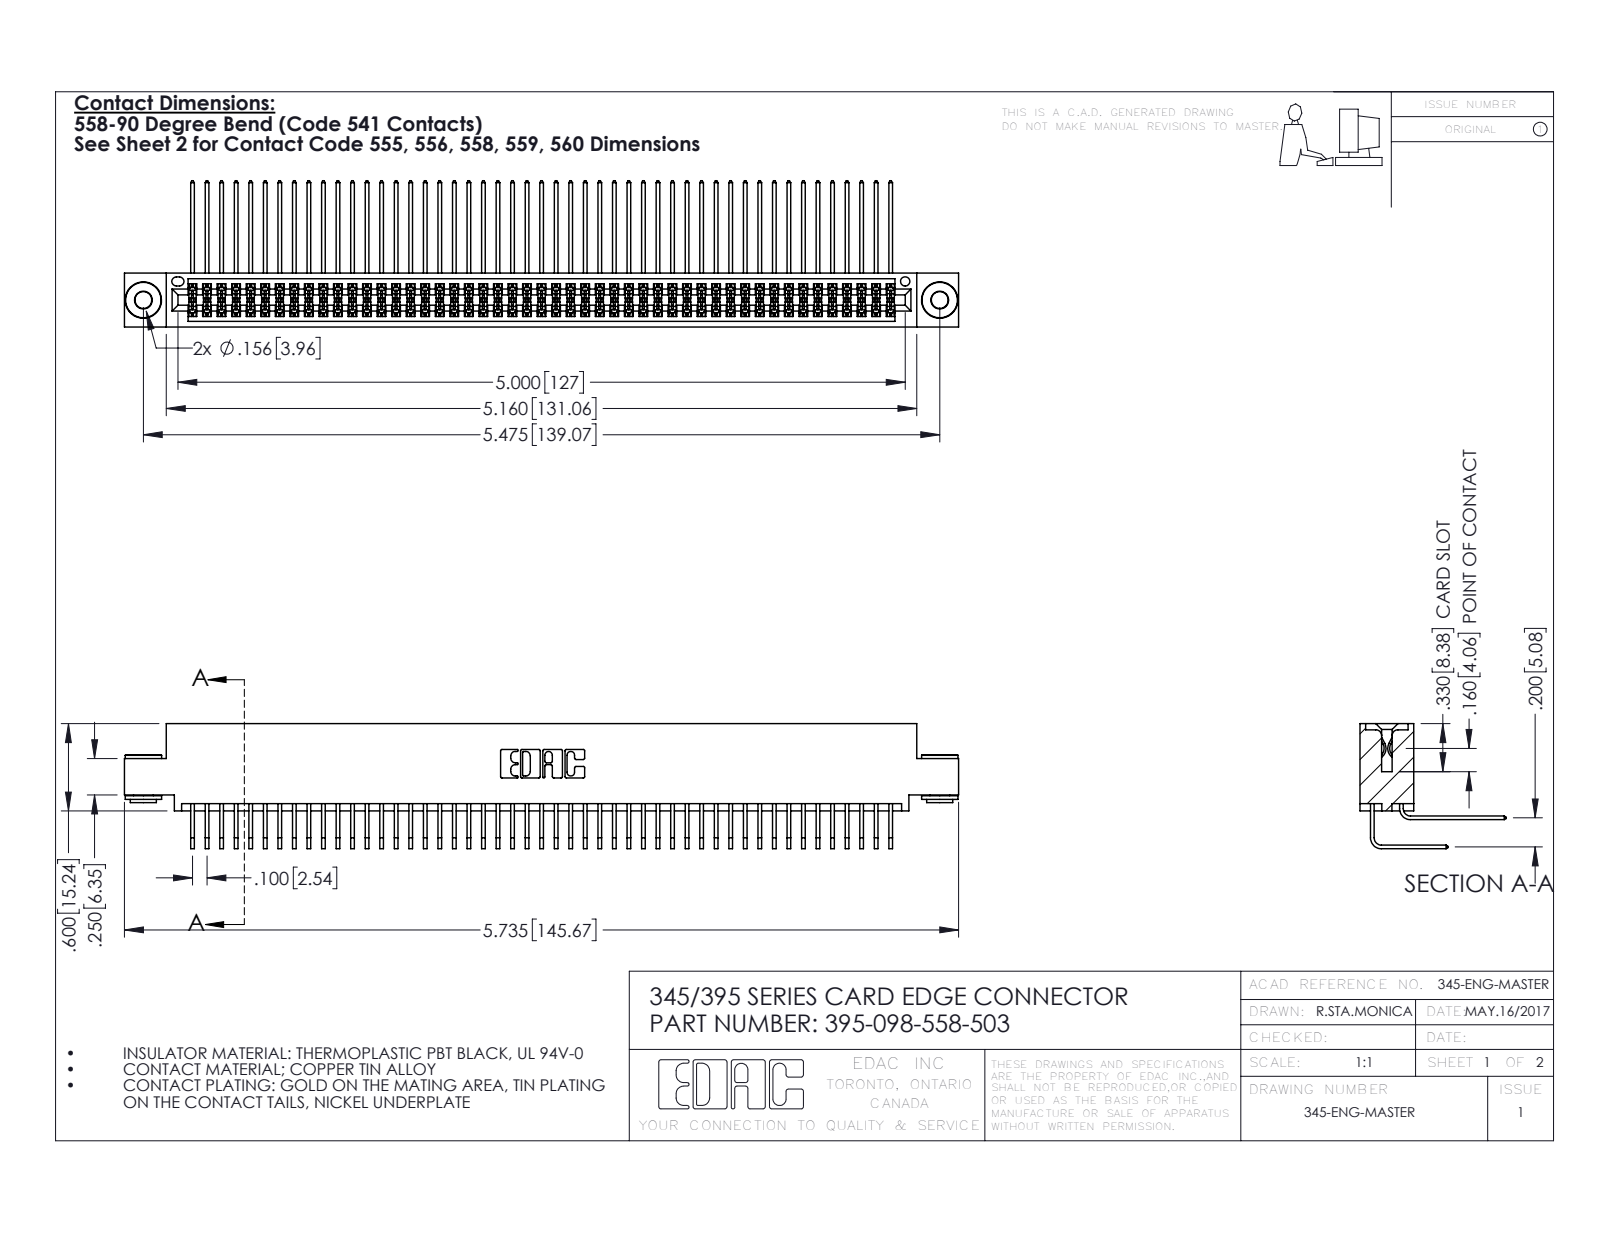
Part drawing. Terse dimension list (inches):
name: 345-292-001_558 Tail - 2; 345 Part_0.110 Offset - 0.156 Dia-TH; 345-250-002_345-250-002-102; 395-098-558-503 (+1 more)
written by: SolidWorks 2016 (CONFIG_CONTROL_DESIGN)
unit: in
bodies: 101 solids, 5264 faces (3524 planar, 1732 cylindrical, 8 other)
size: 5.735 × 1.005 × 0.859
volume: 0.899 in³; area: 38.53 in²
holes: 2× ⌀0.116, 2× ⌀0.156, 1× ⌀0.064
bosses: 2× ⌀0.25, 2× ⌀0.18, 2× ⌀0.136
rounds: 148× R0.006, 22× R0.01, 6× R0.007, 6× R0.031, 3× R0.026, 2× R0.014, 2× R0.019, 2× R0.022
face distances: 0.072, 0.298, 0.2, 0.025, 0.37, 0.098, 0.272, 0.225, 0.025, 0.175
hole spacings: 0.27, 5.239, 5.475
